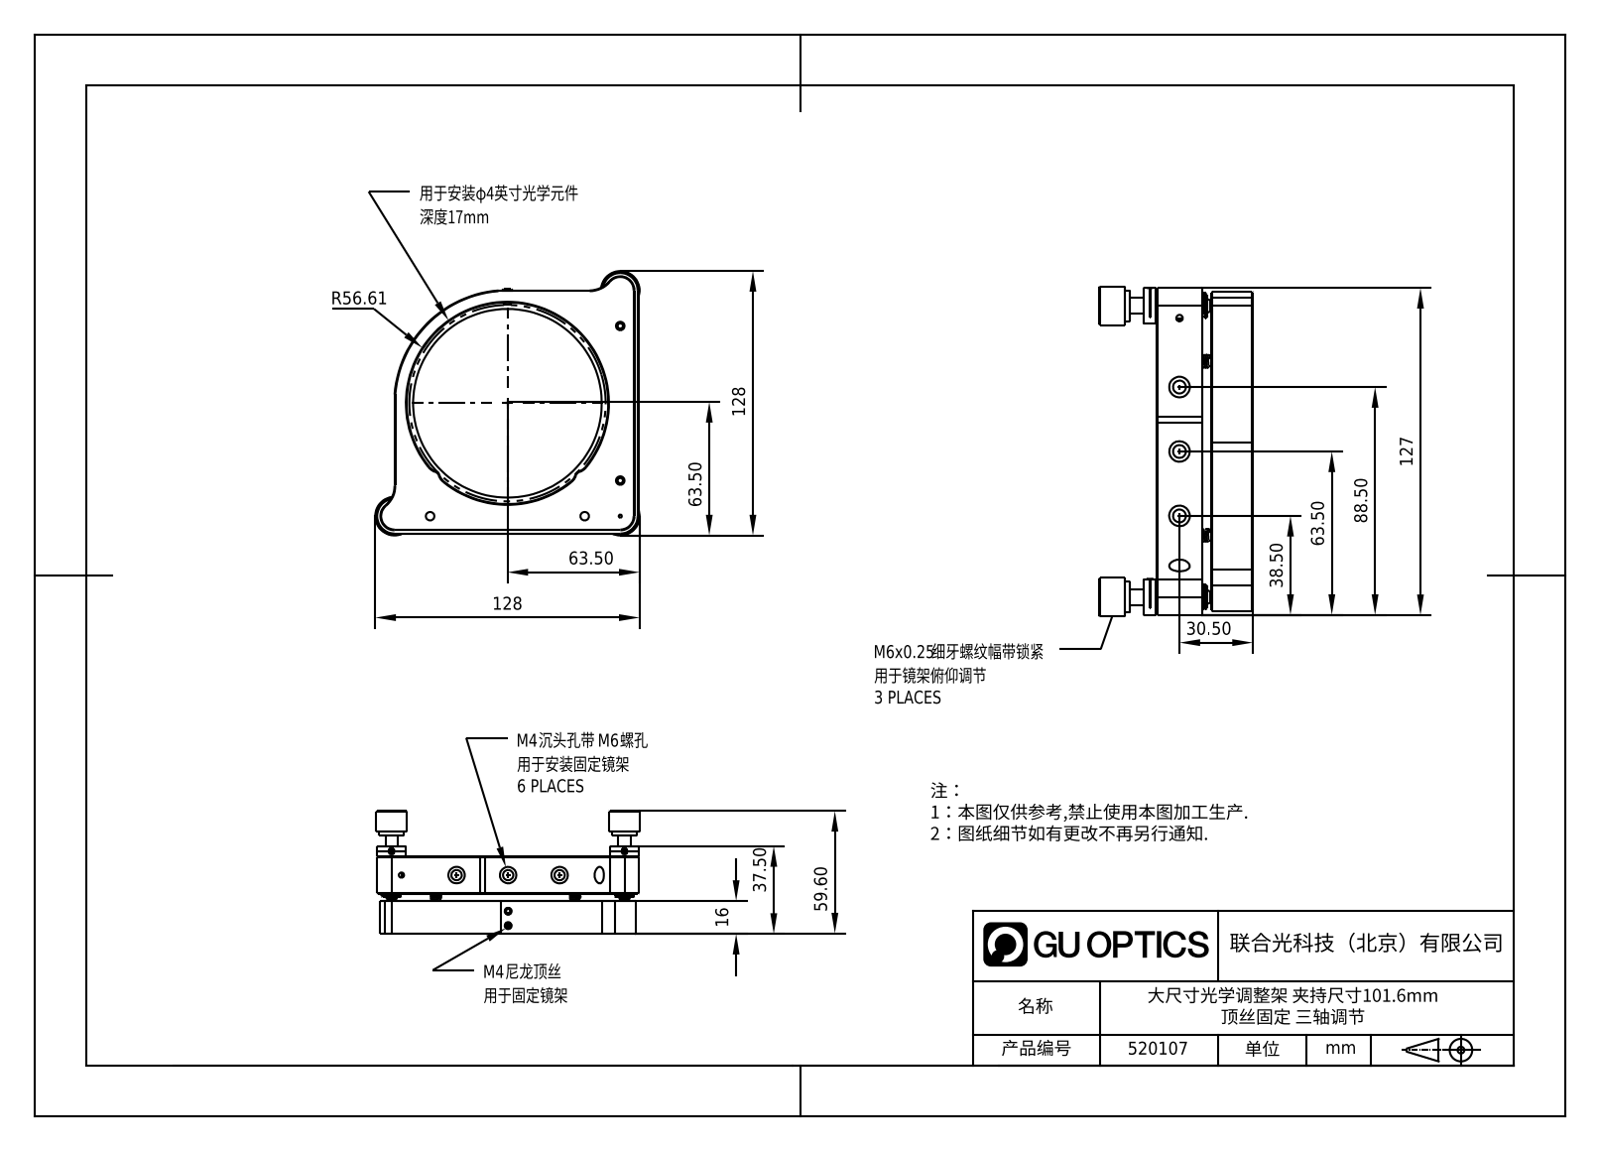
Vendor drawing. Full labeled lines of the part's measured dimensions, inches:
Part name (STEP PRODUCT): 520107
STEP written by: SolidWorks 2020 (CONFIG_CONTROL_DESIGN)
Units: inches
Bodies: 0 solids, 337 faces (166 planar, 89 cylindrical, 82 other)
Overall size (bounding box): 5.039 × 5.039 × 2.35
Round holes (diameter × count): ⌀0.197 ×6, ⌀0.315 ×6, ⌀0.256 ×4, ⌀0.374 ×3, ⌀0.098 ×2, ⌀0.157 ×1
Round bosses / shafts (diameter × count): ⌀0.13 ×6, ⌀0.118 ×4, ⌀0.079 ×4, ⌀0.591 ×3, ⌀0.551 ×3, ⌀0.236 ×3, ⌀0.157 ×3, ⌀0.315 ×2
Partial cylindrical surfaces — rounded edges, fillets, slot ends (radius × count): R0.197 ×11, R0.041 ×8, R0.217 ×3, R0.098 ×2, R0.315 ×2, R0.394 ×2, R0.008 ×1, R2.008 ×1
Main face-to-face distances: 0.63, 0.846, 1.476, 0.768, 0.138, 0.709, 0.059, 0.039, 4.665, 4.724
Hole centre spacings: 0.984, 0.846, 0.945, 1.053, 1.969, 2.037, 2.657, 3.022
